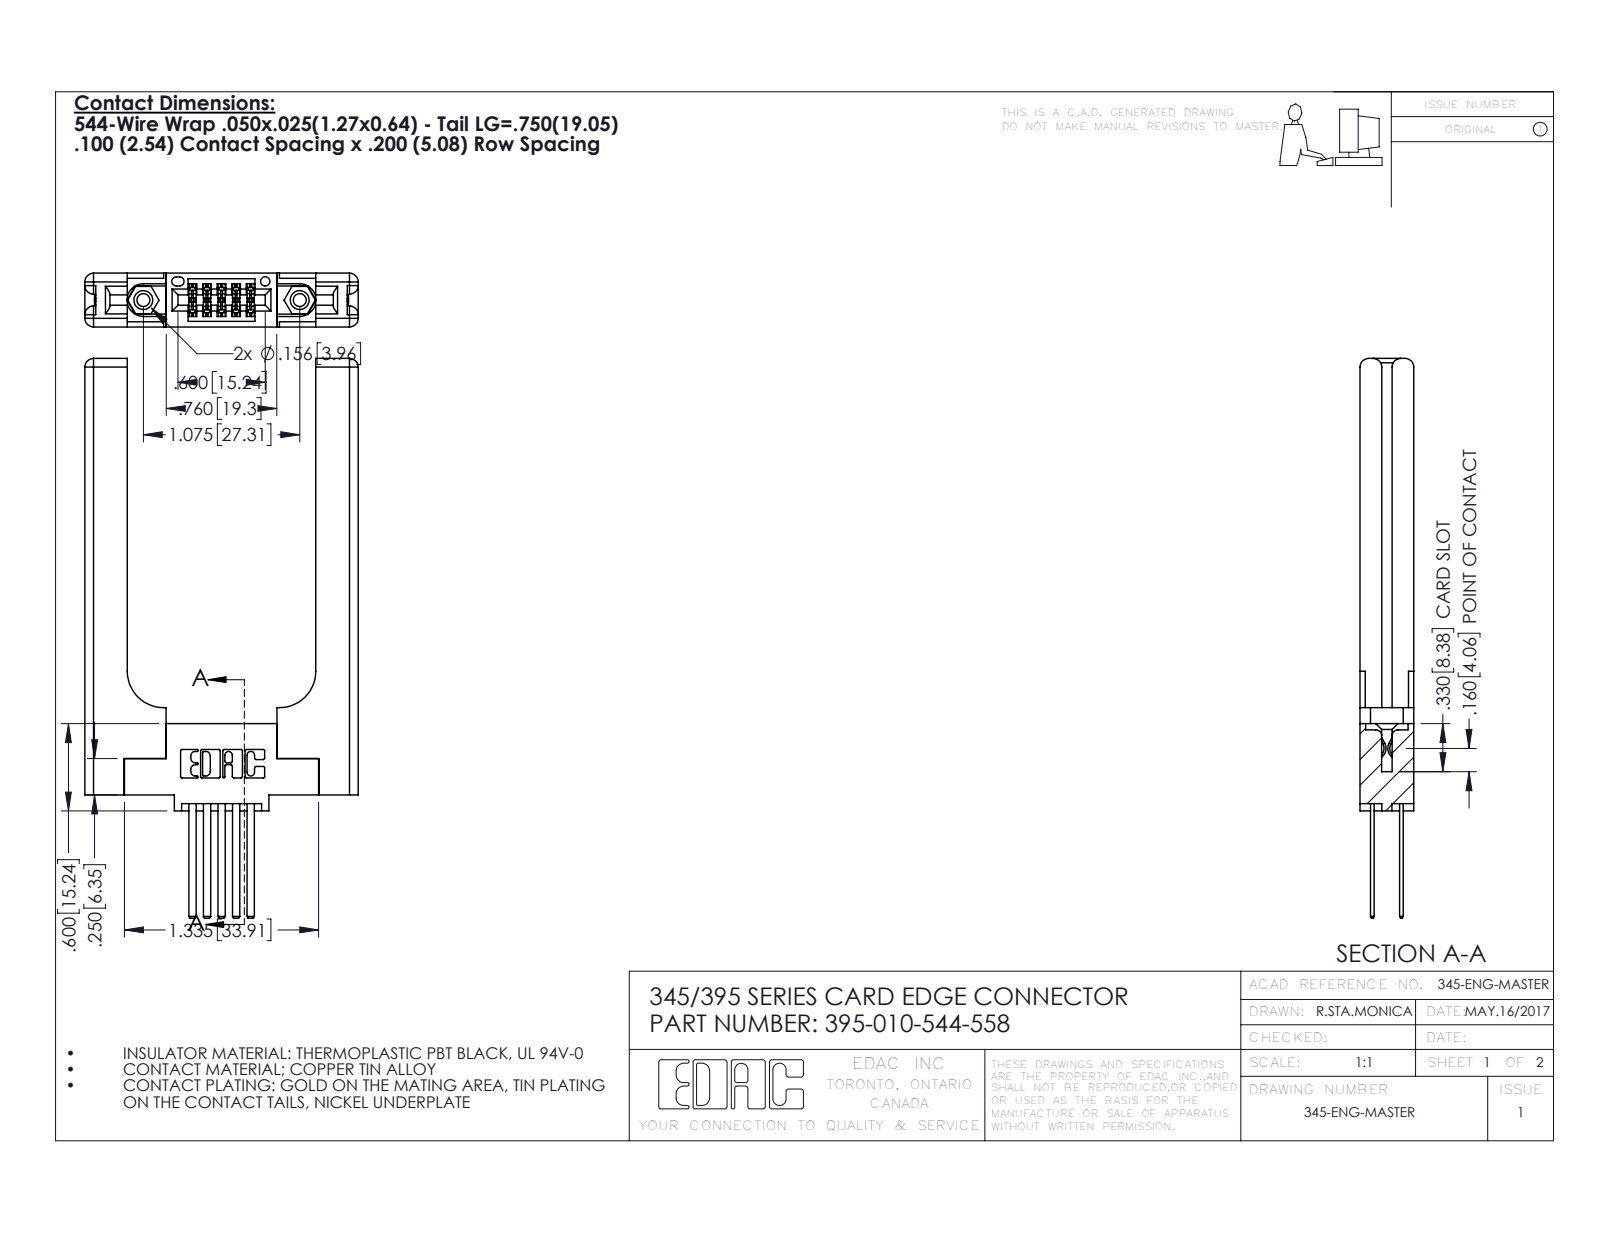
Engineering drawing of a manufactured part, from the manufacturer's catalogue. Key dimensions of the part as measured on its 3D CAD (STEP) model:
Part name (STEP PRODUCT): 345-292-001_345-293-144; 345-250-001_345-250-001-102; 395-010-544-558; 345 Part_0.110 Offset - 0.156 Dia-TH (+1 more)
STEP written by: SolidWorks 2016 (CONFIG_CONTROL_DESIGN)
Units: inches
Bodies: 15 solids, 826 faces (522 planar, 244 cylindrical, 60 other)
Overall size (bounding box): 3.847 × 1.879 × 0.37
Volume: 0.783 in³ · Surface area: 17.5 in²
Round holes (diameter × count): ⌀0.089 ×2, ⌀0.125 ×2, ⌀0.156 ×2, ⌀0.064 ×1
Round bosses / shafts (diameter × count): ⌀0.155 ×2
Partial cylindrical surfaces — rounded edges, fillets, slot ends (radius × count): R0.01 ×22, R0.06 ×16, R0.006 ×15, R0.007 ×6, R0.031 ×6, R0.026 ×3, R0.014 ×2, R0.019 ×2
Main face-to-face distances: 0.37, 0.15, 0.072, 0.22, 0.148, 0.077, 0.298, 1.296, 0.098, 0.272
Hole centre spacings: 0.27, 0.847, 1.075
